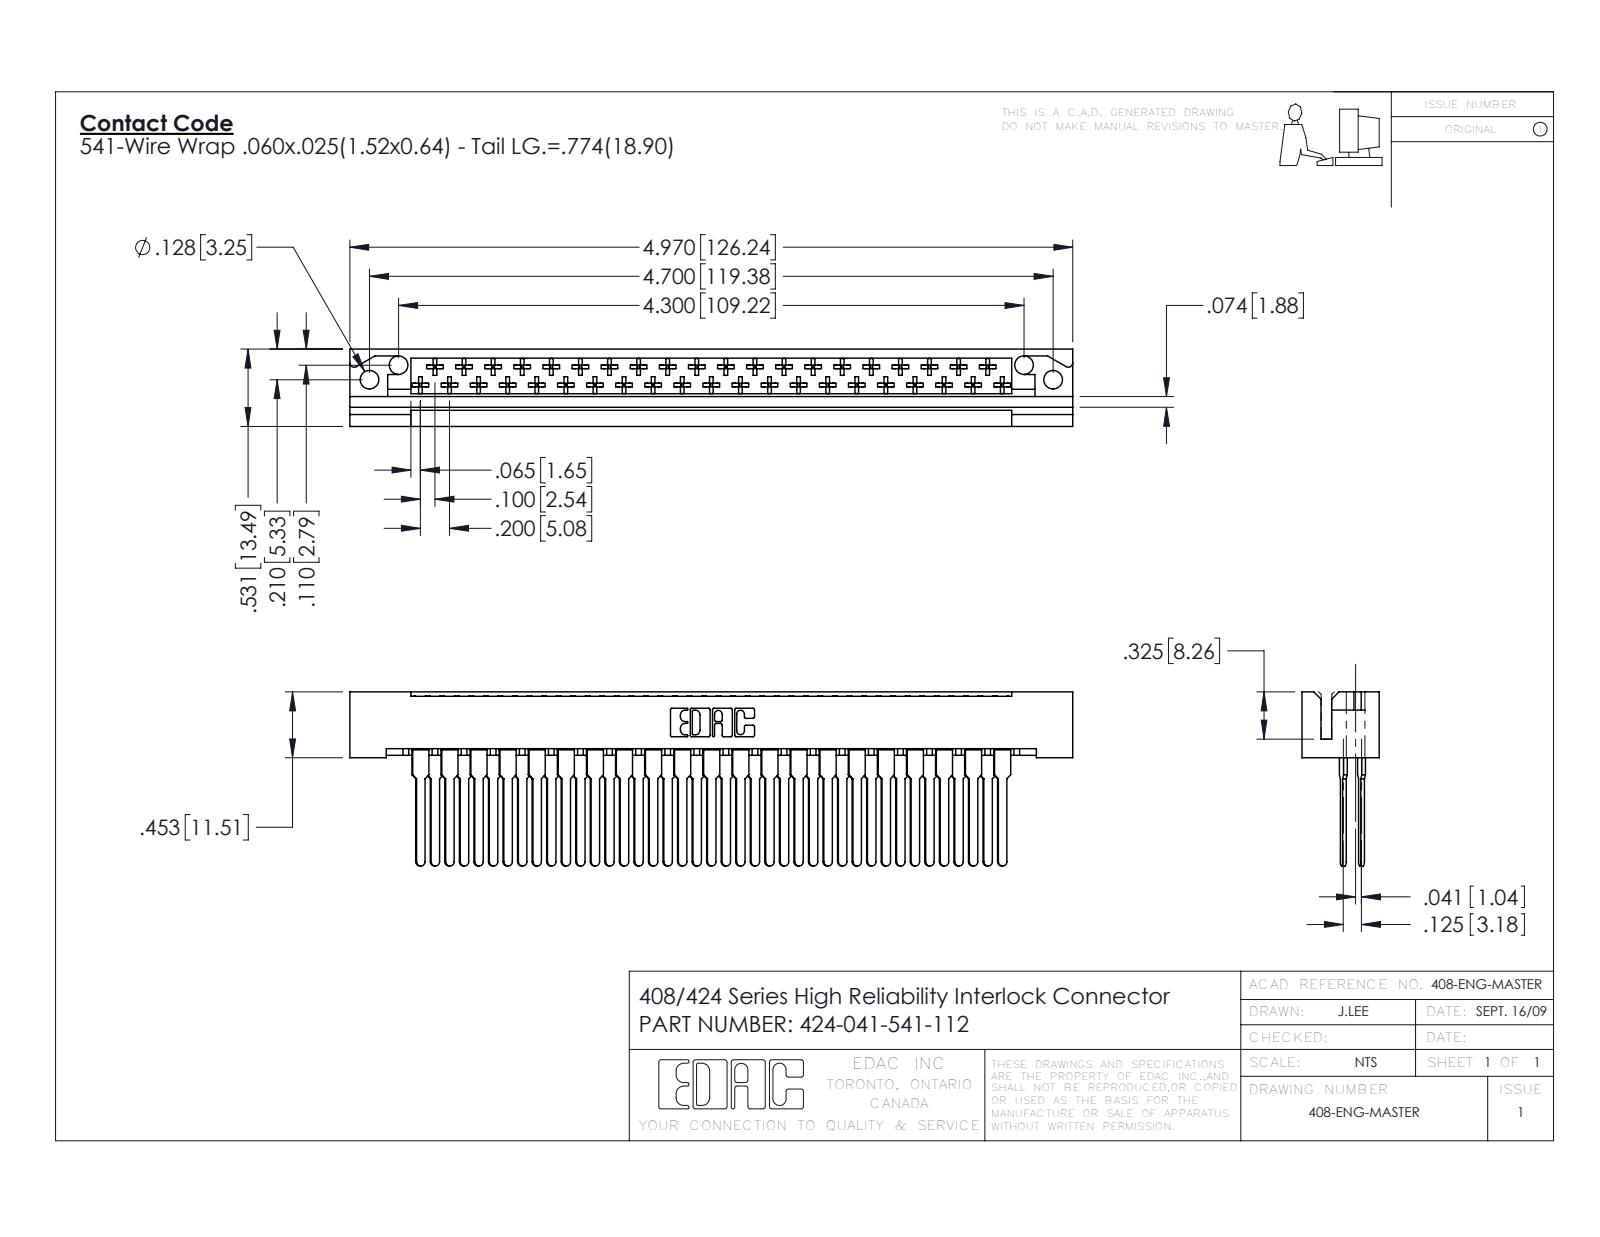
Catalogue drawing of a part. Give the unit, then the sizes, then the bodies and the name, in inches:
Units: inches
Overall size (bounding box): 4.97 × 1.197 × 0.531
Round holes (diameter × count): ⌀0.128 ×4
Partial cylindrical surfaces — rounded edges, fillets, slot ends (radius × count): R0.01 ×246, R0.02 ×43, R0.03 ×43, R0.01 ×22, R0.007 ×6, R0.031 ×6, R0.026 ×3
Main face-to-face distances: 0.025, 0.531, 0.125, 0.4, 0.1, 0.235, 0.259, 0.272, 0.025, 0.296
Hole centre spacings: 0.224, 4.501, 4.3, 4.7
Volume: 0.89 in³ · Surface area: 31.43 in²
Bodies: 42 solids, 2318 faces (1729 planar, 425 cylindrical, 164 other)
Part name (STEP PRODUCT): 424 Part_041; 408-290-001_408-290-141; 424-047-541-112
STEP written by: SolidWorks 2016 (CONFIG_CONTROL_DESIGN)
